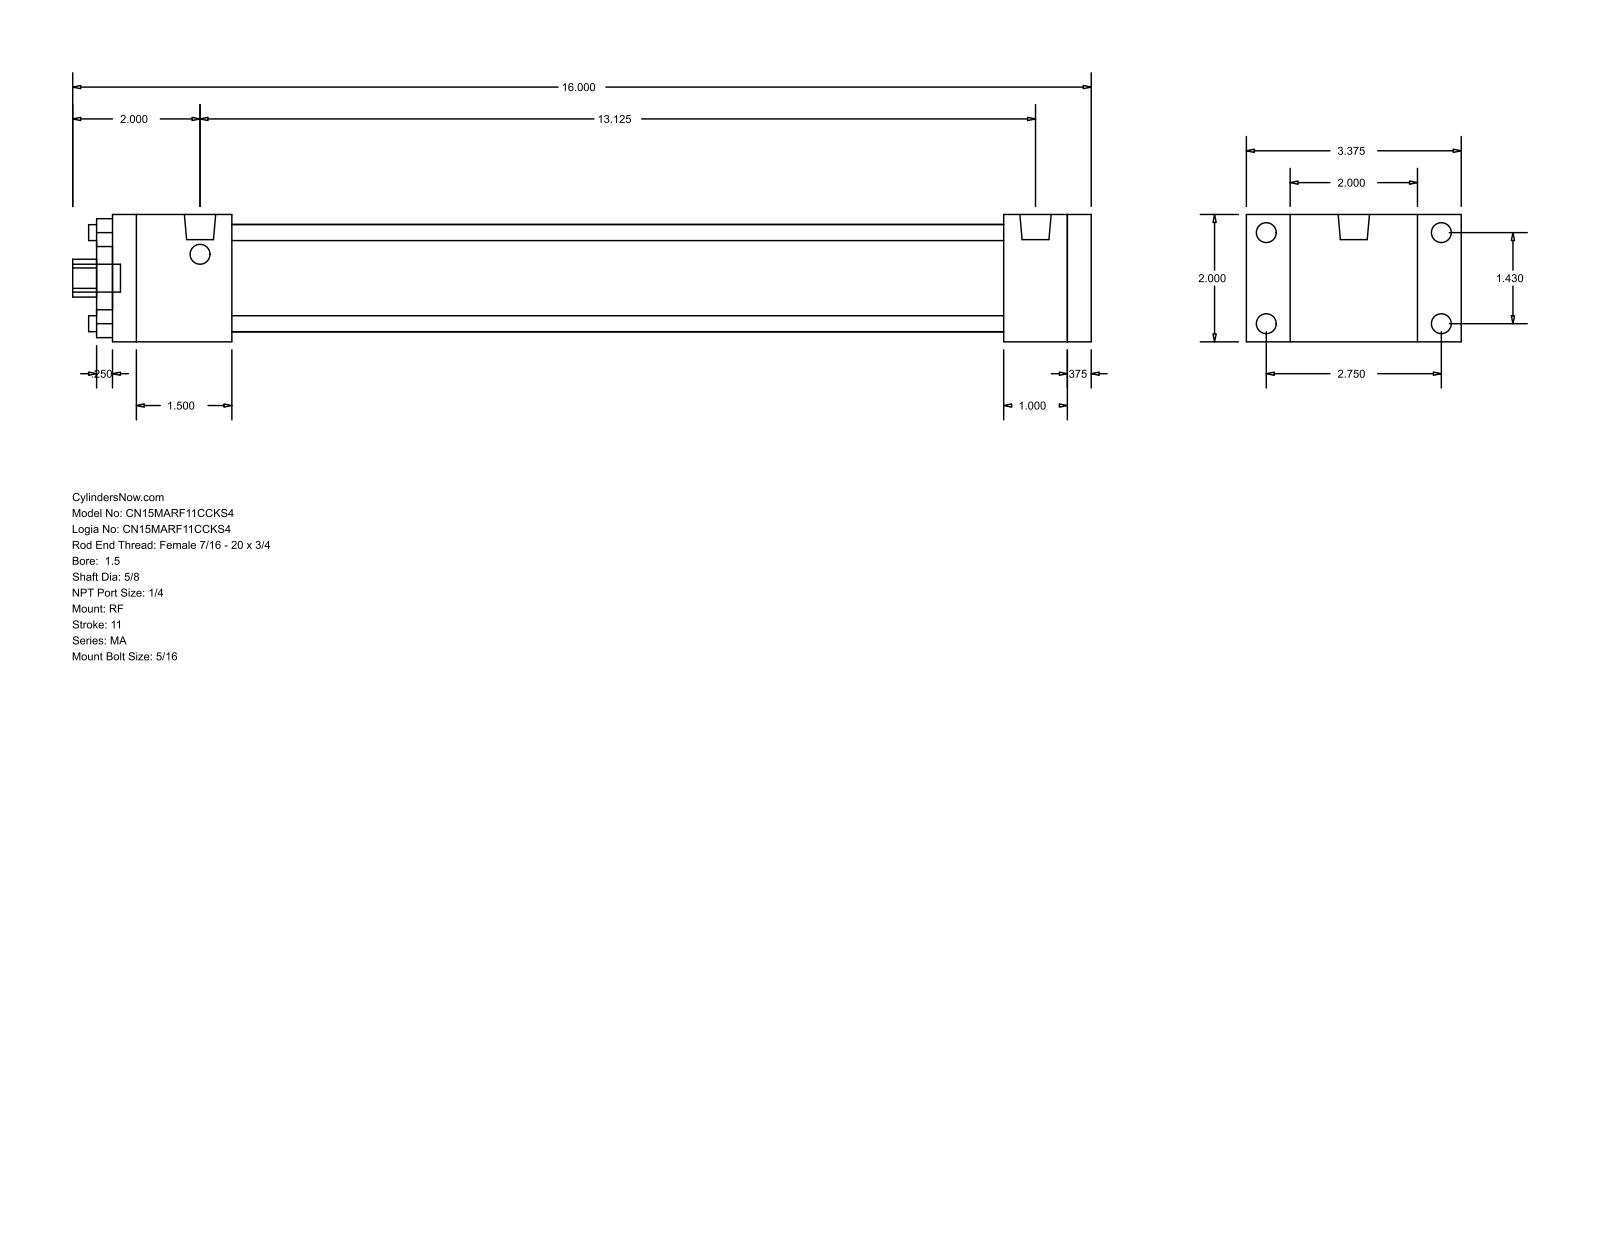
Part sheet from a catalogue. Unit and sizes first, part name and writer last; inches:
Units: inches
Overall size (bounding box): 16 × 3.375 × 2
Round holes (diameter × count): ⌀0.25 ×4, ⌀0.625 ×1, ⌀1.125 ×1, ⌀1.69 ×1
Round bosses / shafts (diameter × count): ⌀0.313 ×8, ⌀0.492 ×2, ⌀0.437 ×1
Partial cylindrical surfaces — rounded edges, fillets, slot ends (radius × count): R0.297 ×1
Main face-to-face distances: 2, 0.375, 15, 15.375, 14, 1, 1.375, 1.875, 12.125, 13.125
Hole centre spacings: 1.011, 1.43, 2.022
Bodies: 0 solids, 92 faces (64 planar, 28 cylindrical, 0 other)
Part name (STEP PRODUCT): MA_RF__0150_0.625
STEP written by: GSSL Pune (CONFIG_CONTROL_DESIGN)
